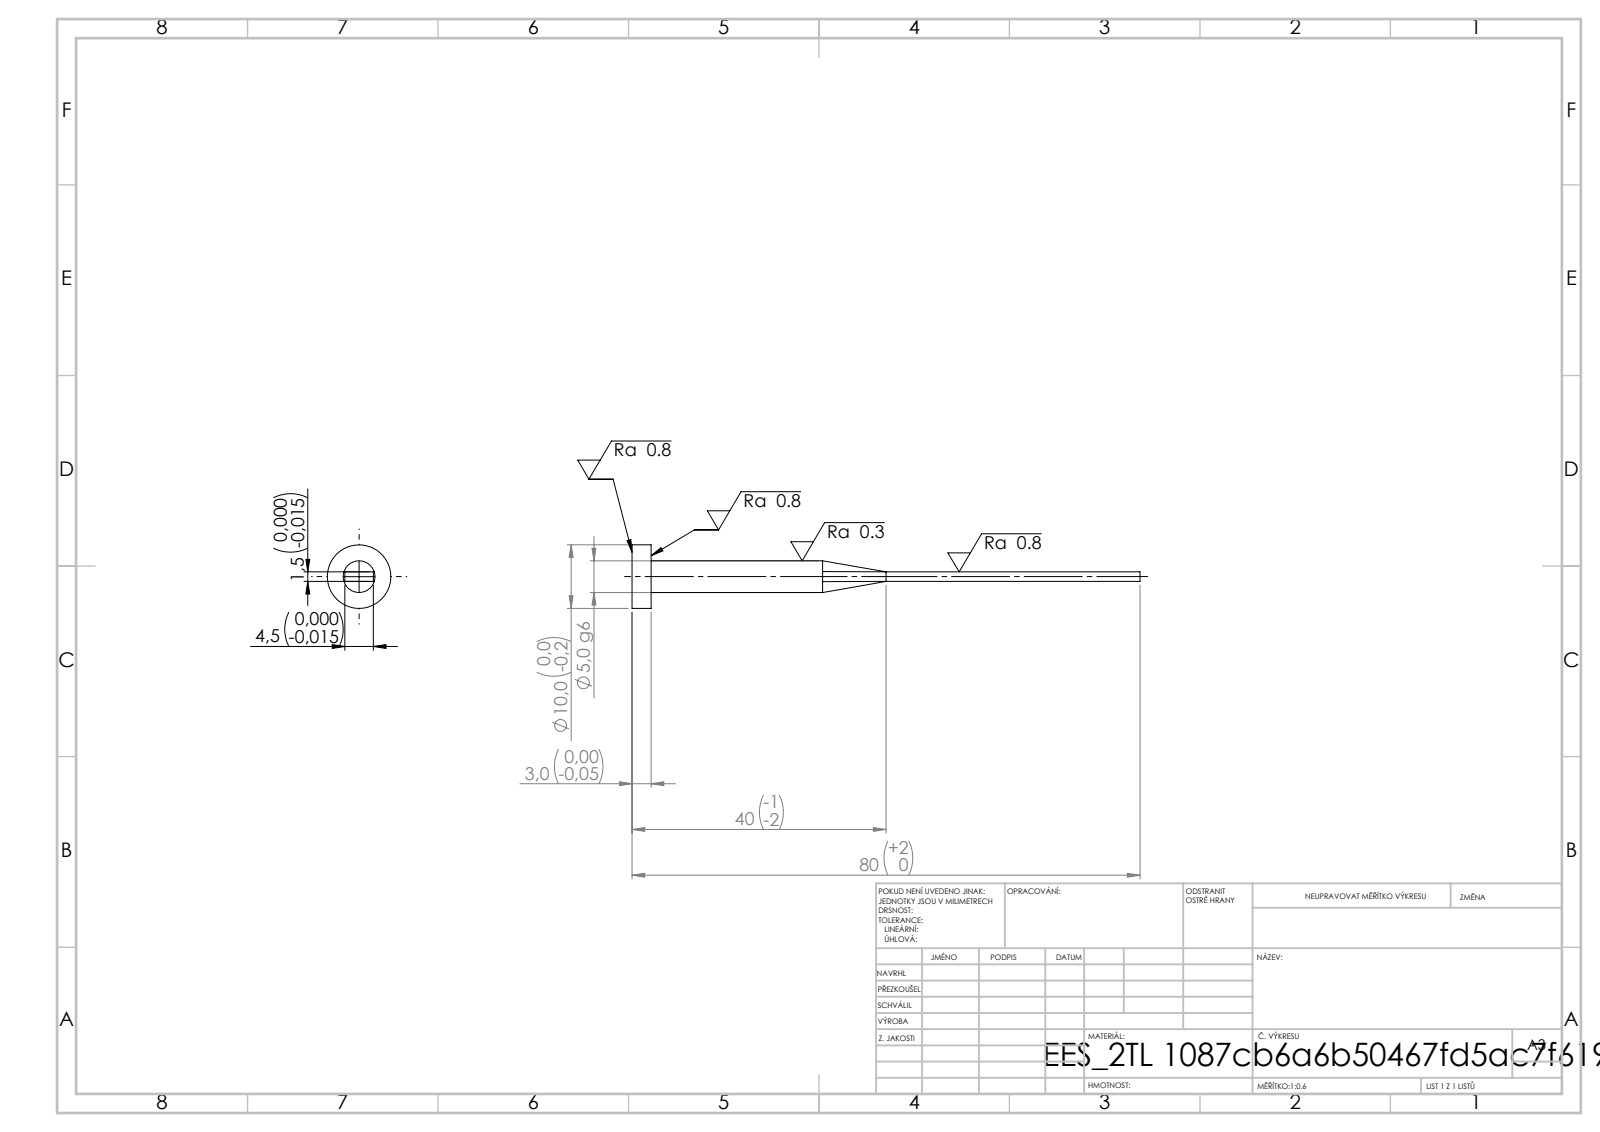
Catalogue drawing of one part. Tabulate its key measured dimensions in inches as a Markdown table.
| quantity | value |
| --- | --- |
| STEP written by | SolidWorks 2019 (CONFIG_CONTROL_DESIGN) |
| units | inches |
| bodies | 1 solid, 15 faces (7 planar, 4 cylindrical, 4 other) |
| overall size | 3.15 × 0.394 × 0.394 |
| volume | 0.071 in³ |
| surface area | 1.979 in² |
| round bosses / shafts (diameter × count) | 0.394 × 1, 0.197 × 1 |
| main face-to-face distances | 0.059, 0.177, 0.118, 3.15, 3.031 |
